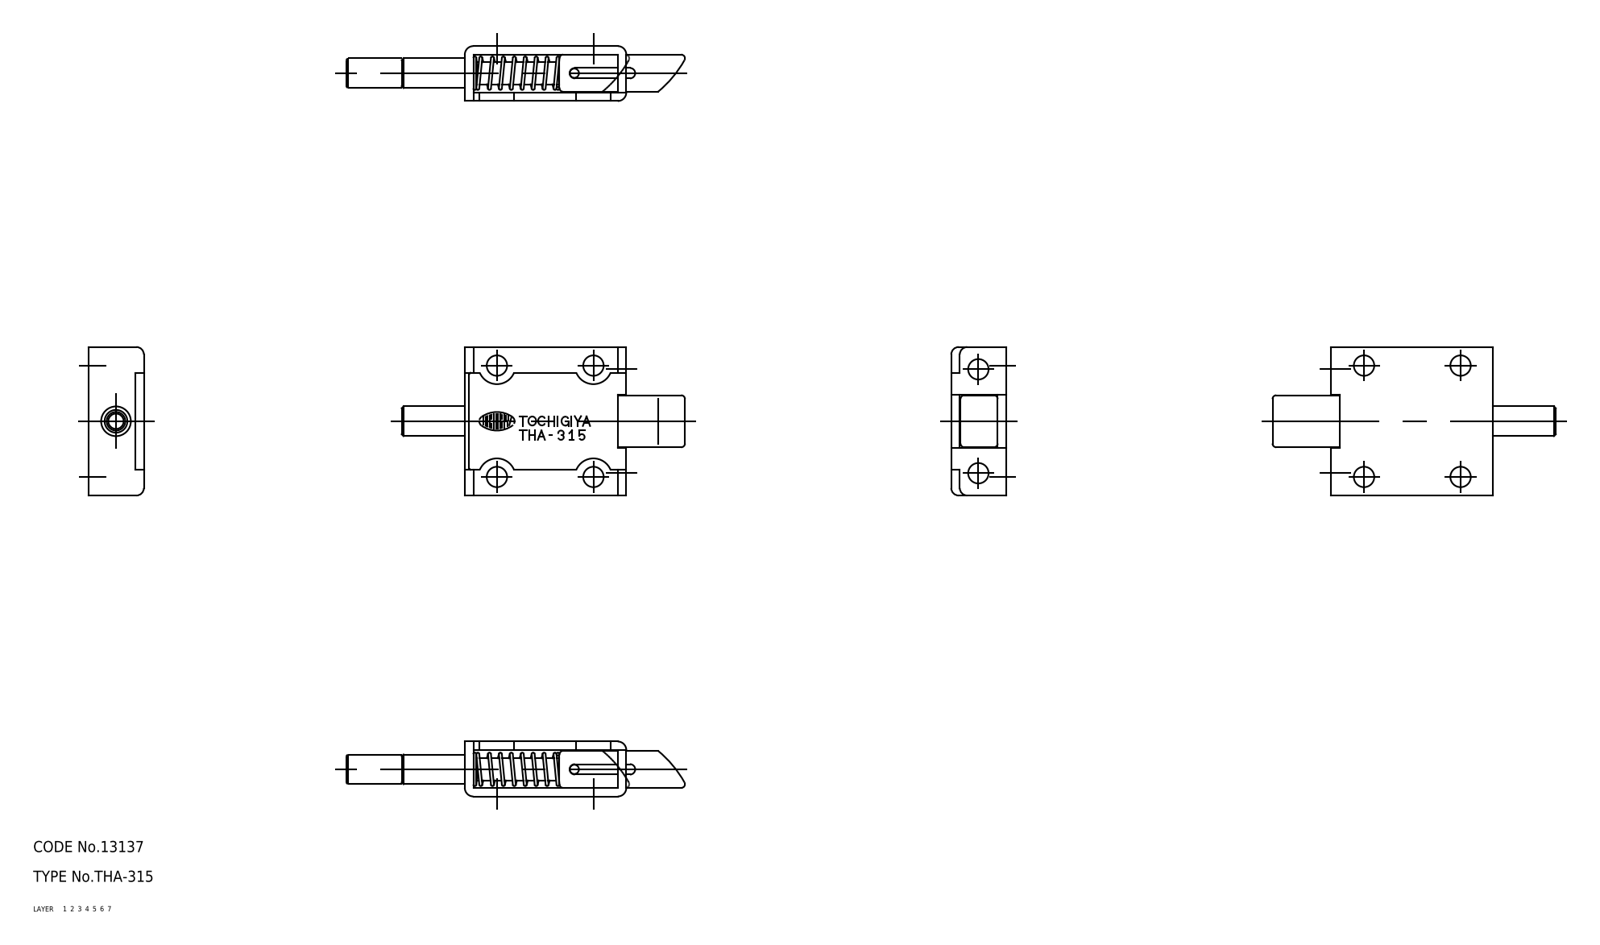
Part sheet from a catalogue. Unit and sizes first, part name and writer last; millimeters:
Units: millimetres
Overall size (bounding box): 76.3 × 40 × 14.8
Volume: 12 348 mm³ · Surface area: 11 708 mm²
Bodies: 5 solids, 117 faces (0 planar, 0 cylindrical, 117 other)
Part name (STEP PRODUCT): housing; spring; pin; latch (+2 more)
STEP written by: CADfix (AUTOMOTIVE_DESIGN)
